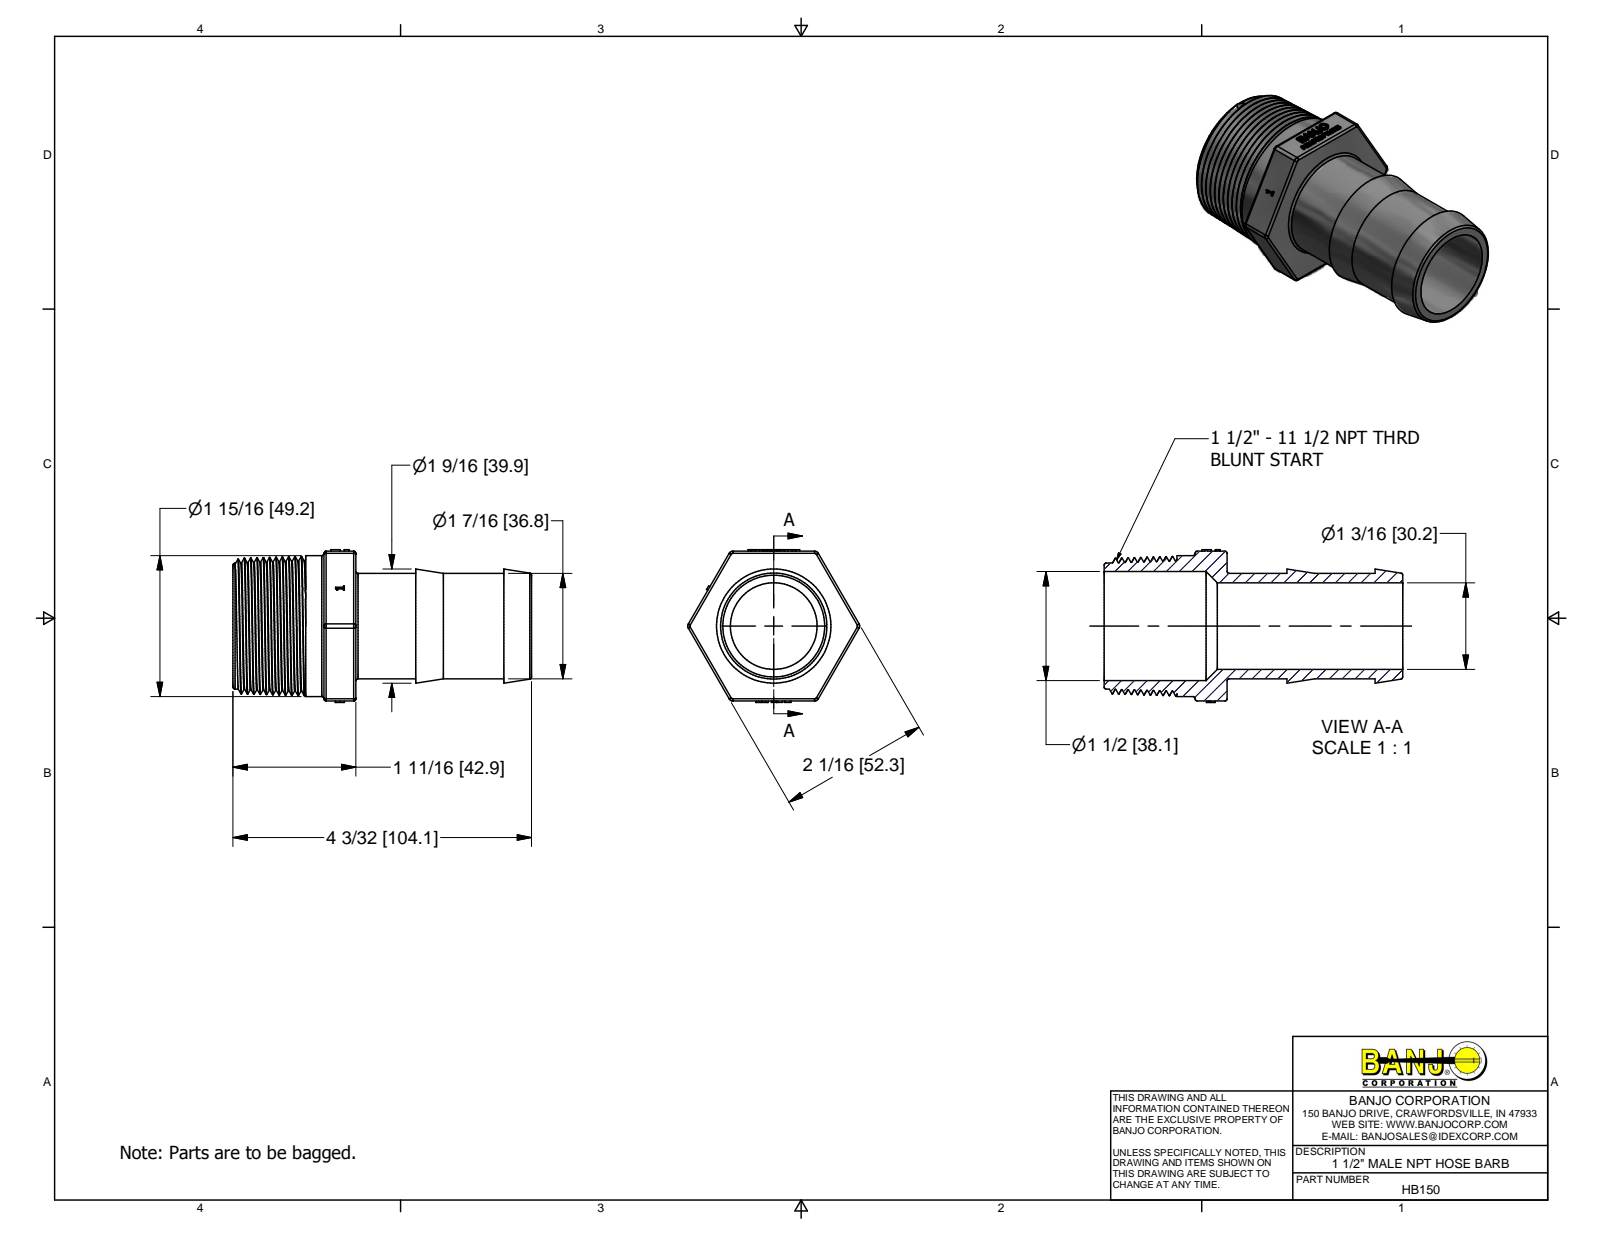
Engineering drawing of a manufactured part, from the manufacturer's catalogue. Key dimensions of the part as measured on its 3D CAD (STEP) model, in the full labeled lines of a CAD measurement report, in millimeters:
Part name (STEP PRODUCT): HB150
STEP written by: Autodesk Inventor 2013 (AUTOMOTIVE_DESIGN)
Units: millimetres
Bodies: 1 solid, 408 faces (229 planar, 23 cylindrical, 156 other)
Overall size (bounding box): 104.1 × 59.9 × 53.3
Volume: 57 470 mm³ · Surface area: 30 630 mm²
Round holes (diameter × count): ⌀30.2 ×1, ⌀38.1 ×1
Round bosses / shafts (diameter × count): ⌀49.2 ×1, ⌀36.8 ×1
Partial cylindrical surfaces — rounded edges, fillets, slot ends (radius × count): R0.8 ×12, R1.5 ×6
Main face-to-face distances: 52.3, 42.9, 104.1, 61.3, 31.8, 11.1, 72.4, 40.4, 63.8, 94.5
